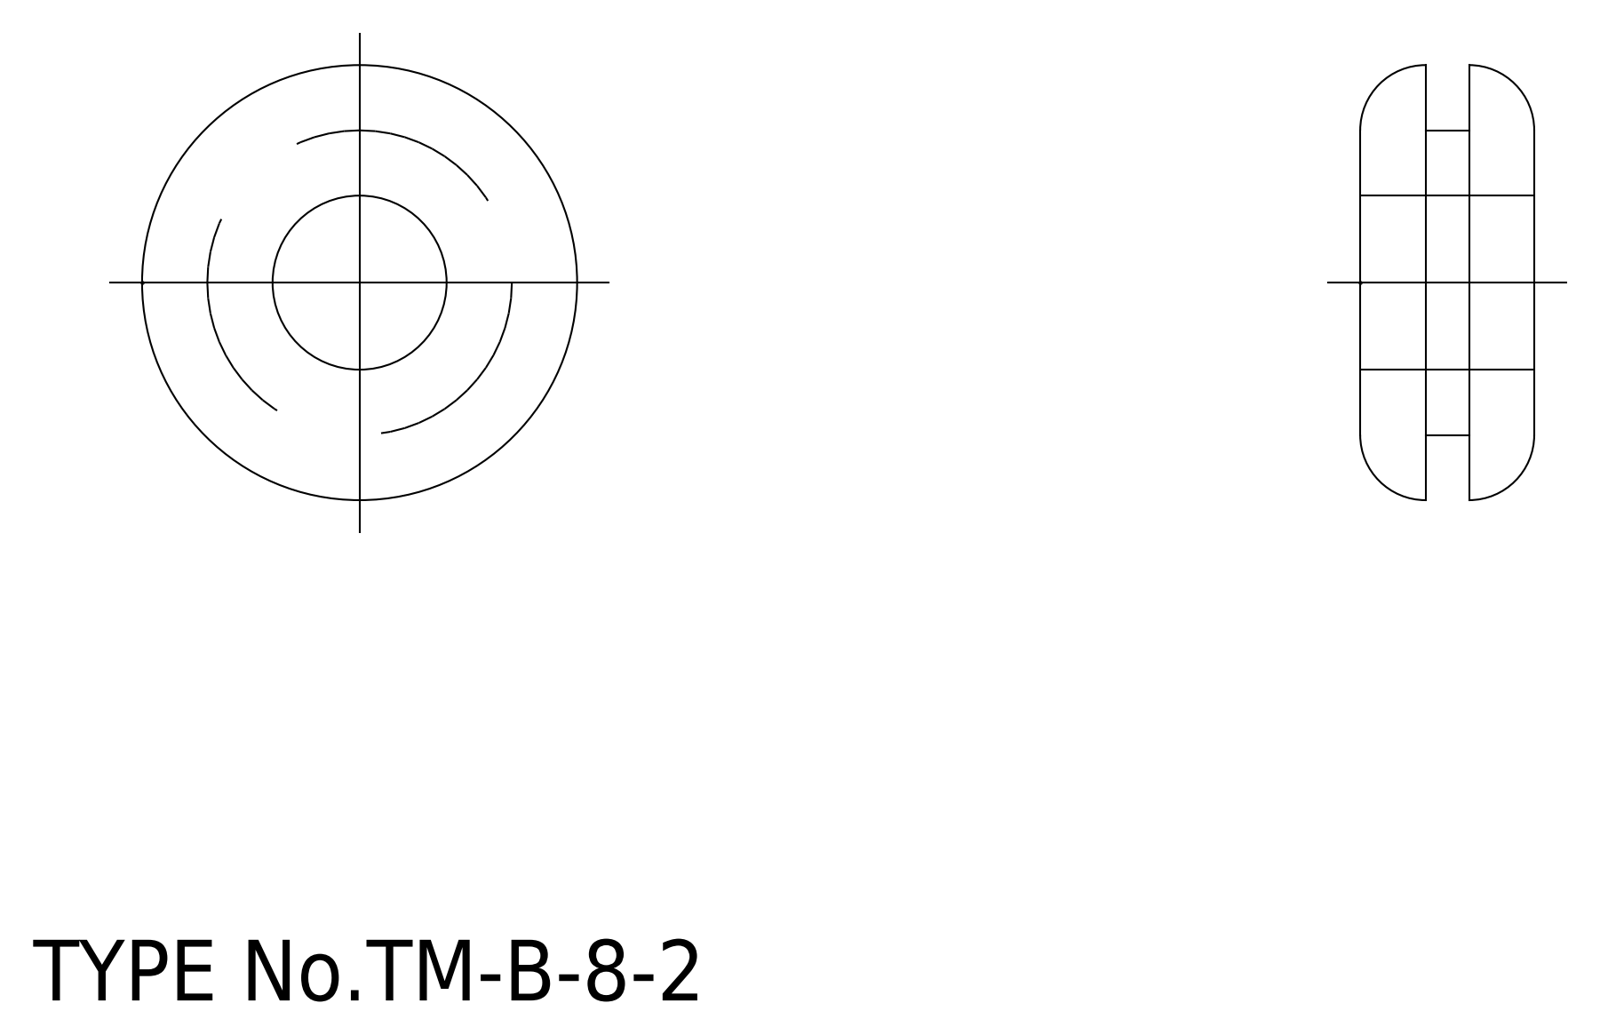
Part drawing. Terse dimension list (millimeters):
name: grommet
written by: CADfix (AUTOMOTIVE_DESIGN)
unit: mm
bodies: 1 solid, 12 faces (0 planar, 0 cylindrical, 12 other)
size: 20 × 20 × 8
volume: 1 568 mm³; area: 1 345 mm²
